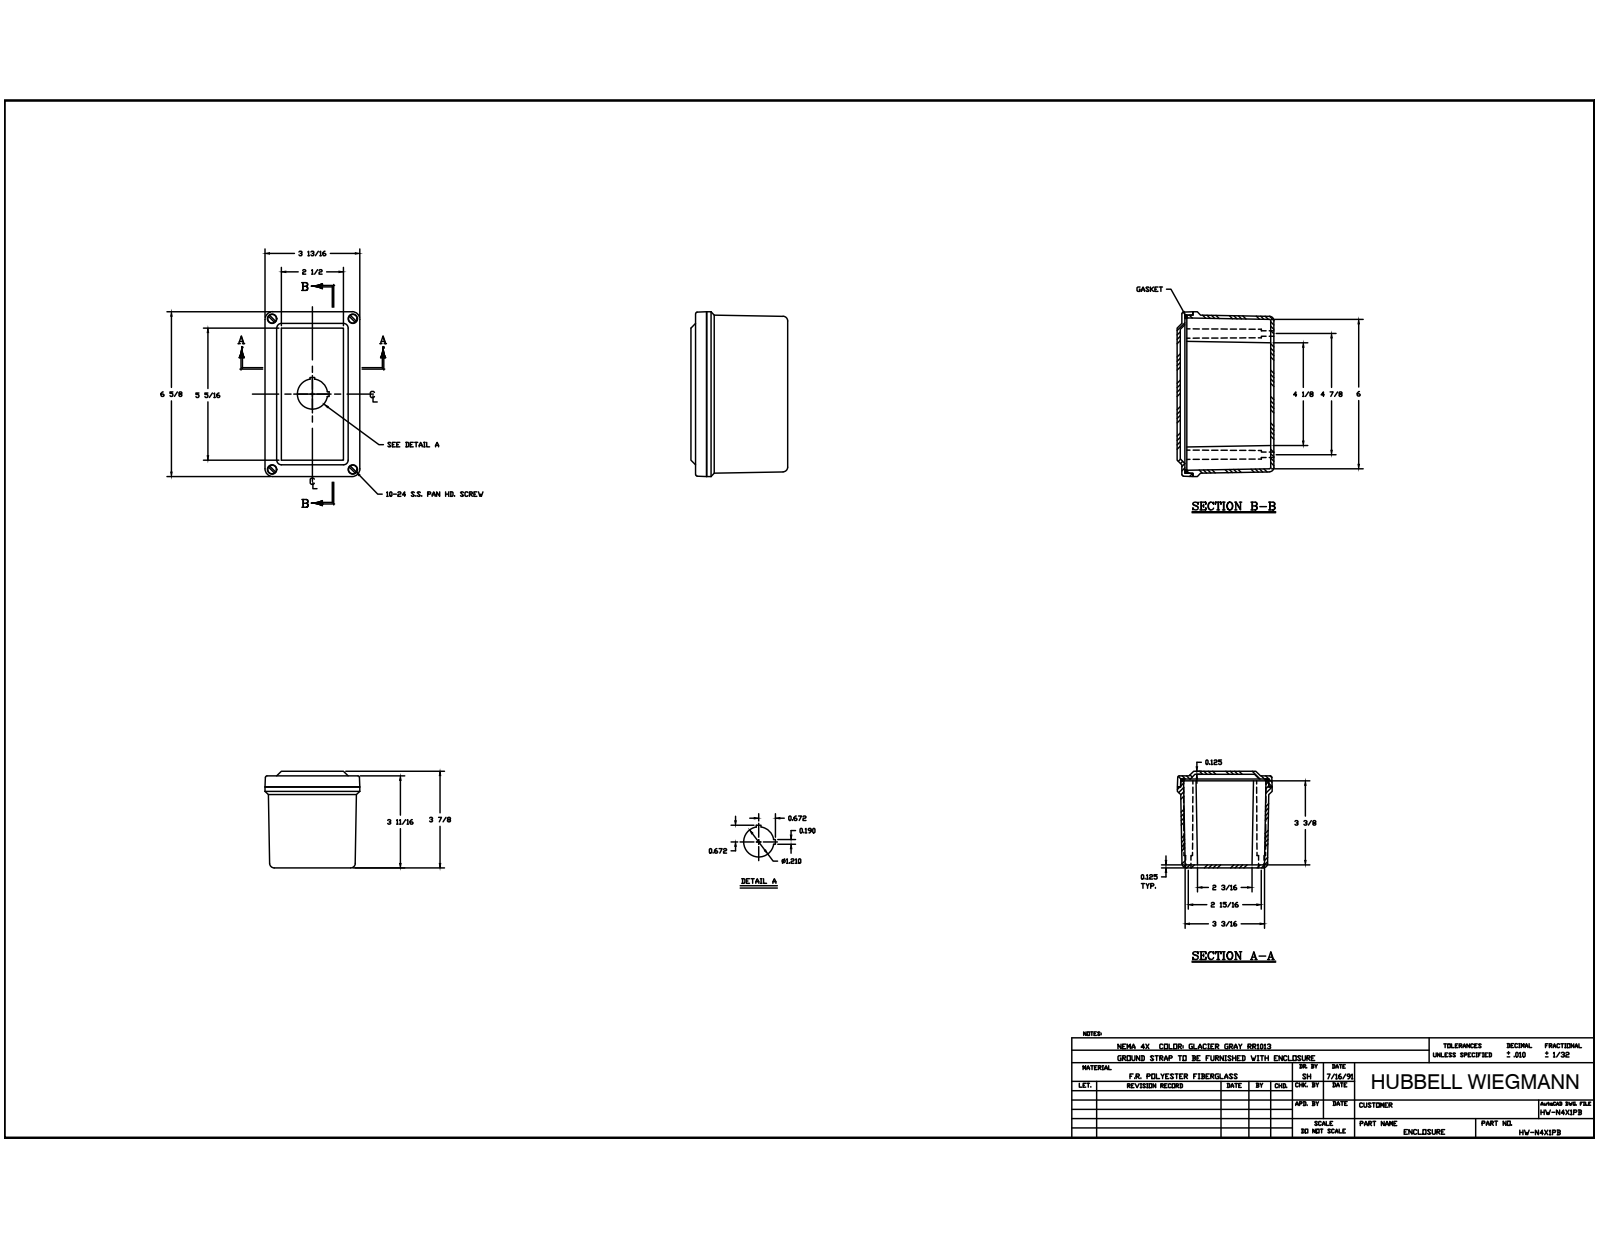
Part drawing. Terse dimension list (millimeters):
name: WPCF644 BOX; 10-24 X 0.4375 DP BRASS INSERT; WPCF1PB CVR; WPCF644 GASKET (+3 more)
written by: Autodesk Inventor 2014 (AUTOMOTIVE_DESIGN)
unit: mm
bodies: 11 solids, 387 faces (189 planar, 106 cylindrical, 92 other)
size: 168.28 × 98.42 × 96.84
volume: 333 792 mm³; area: 171 523 mm²
holes: 8× ⌀5.56, 4× ⌀3.68, 4× ⌀4.83, 4× ⌀9.52, 1× ⌀30.73
bosses: 4× ⌀9.42, 4× ⌀5.54, 4× ⌀4.5
rounds: 20× R0.79, 16× R0.3, 8× R7.94, 4× R1.59, 4× R4.47, 4× R4.76, 4× R5.59, 4× R8.26
face distances: 3.17, 3.42, 95.25, 4.76, 90.49, 12.7, 98.42, 92.08, 1.59, 87.32
hole spacings: 82.54, 15.59, 15.6, 72.28, 80.01, 80.02, 87.35, 87.36
